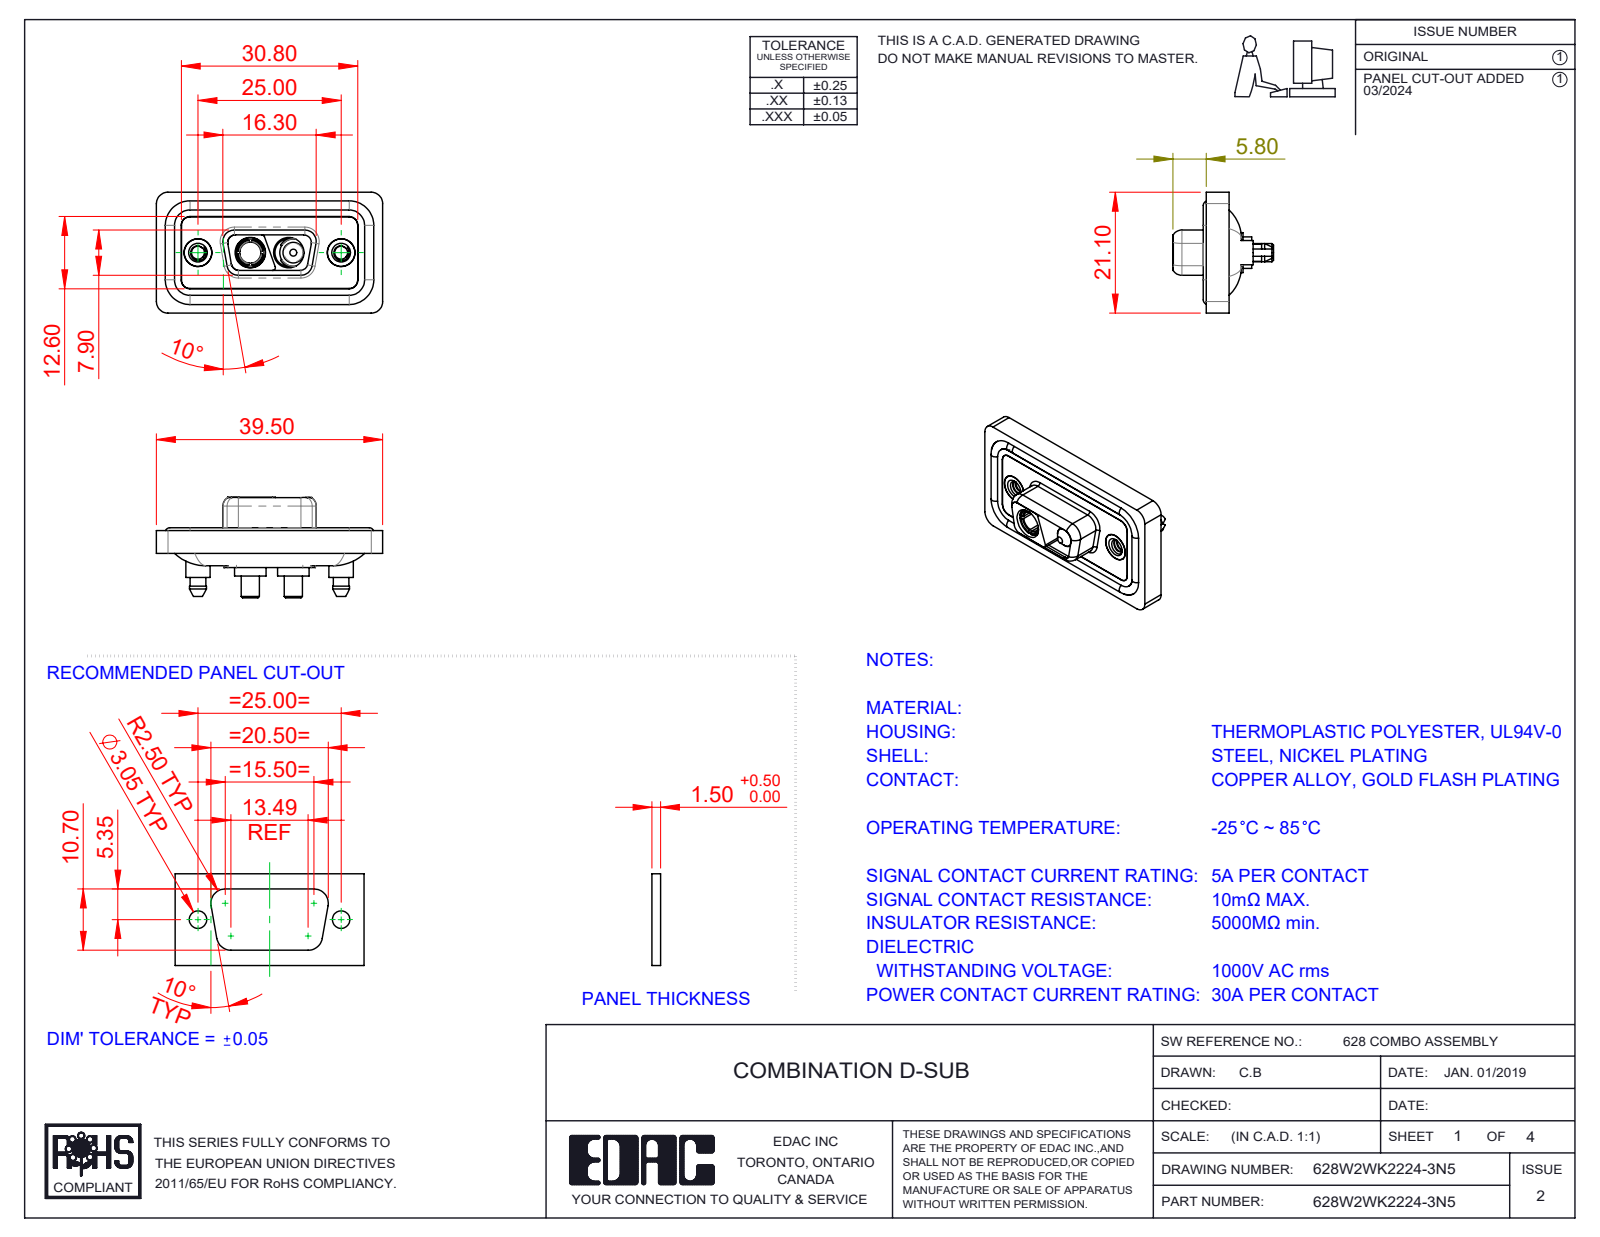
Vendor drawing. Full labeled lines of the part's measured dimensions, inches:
Part name (STEP PRODUCT): 628Combo Waterproof Housing_09 Contacts; 628Combo Shell Front_09 Contacts; 628Combo Threaded Boardlock_5; Power Socket_30A S (+4 more)
STEP written by: SolidWorks 2023 (CONFIG_CONTROL_DESIGN)
Units: inches
Bodies: 11 solids, 550 faces (160 planar, 263 cylindrical, 127 other)
Overall size (bounding box): 1.555 × 0.831 × 0.691
Volume: 0.29 in³ · Surface area: 11.91 in²
Round holes (diameter × count): ⌀0.191 ×4, ⌀0.089 ×2, ⌀0.157 ×2, ⌀0.159 ×2, ⌀0.197 ×2, ⌀0.209 ×2, ⌀0.146 ×1
Round bosses / shafts (diameter × count): ⌀0.063 ×4, ⌀0.217 ×2, ⌀0.213 ×2, ⌀0.205 ×2, ⌀0.195 ×2, ⌀0.189 ×2, ⌀0.187 ×2, ⌀0.167 ×2
Partial cylindrical surfaces — rounded edges, fillets, slot ends (radius × count): R0.059 ×24, R0.079 ×18, R0.063 ×10, R0.053 ×8, R0.02 ×6, R0.01 ×4, R0.024 ×4, R0.026 ×4
Main face-to-face distances: 0.016, 0.043, 0.114, 0.063, 0.02, 0.071, 0.222, 0.059, 0.157, 0.211
Hole centre spacings: 0.36, 0.624, 0.265, 0.984
